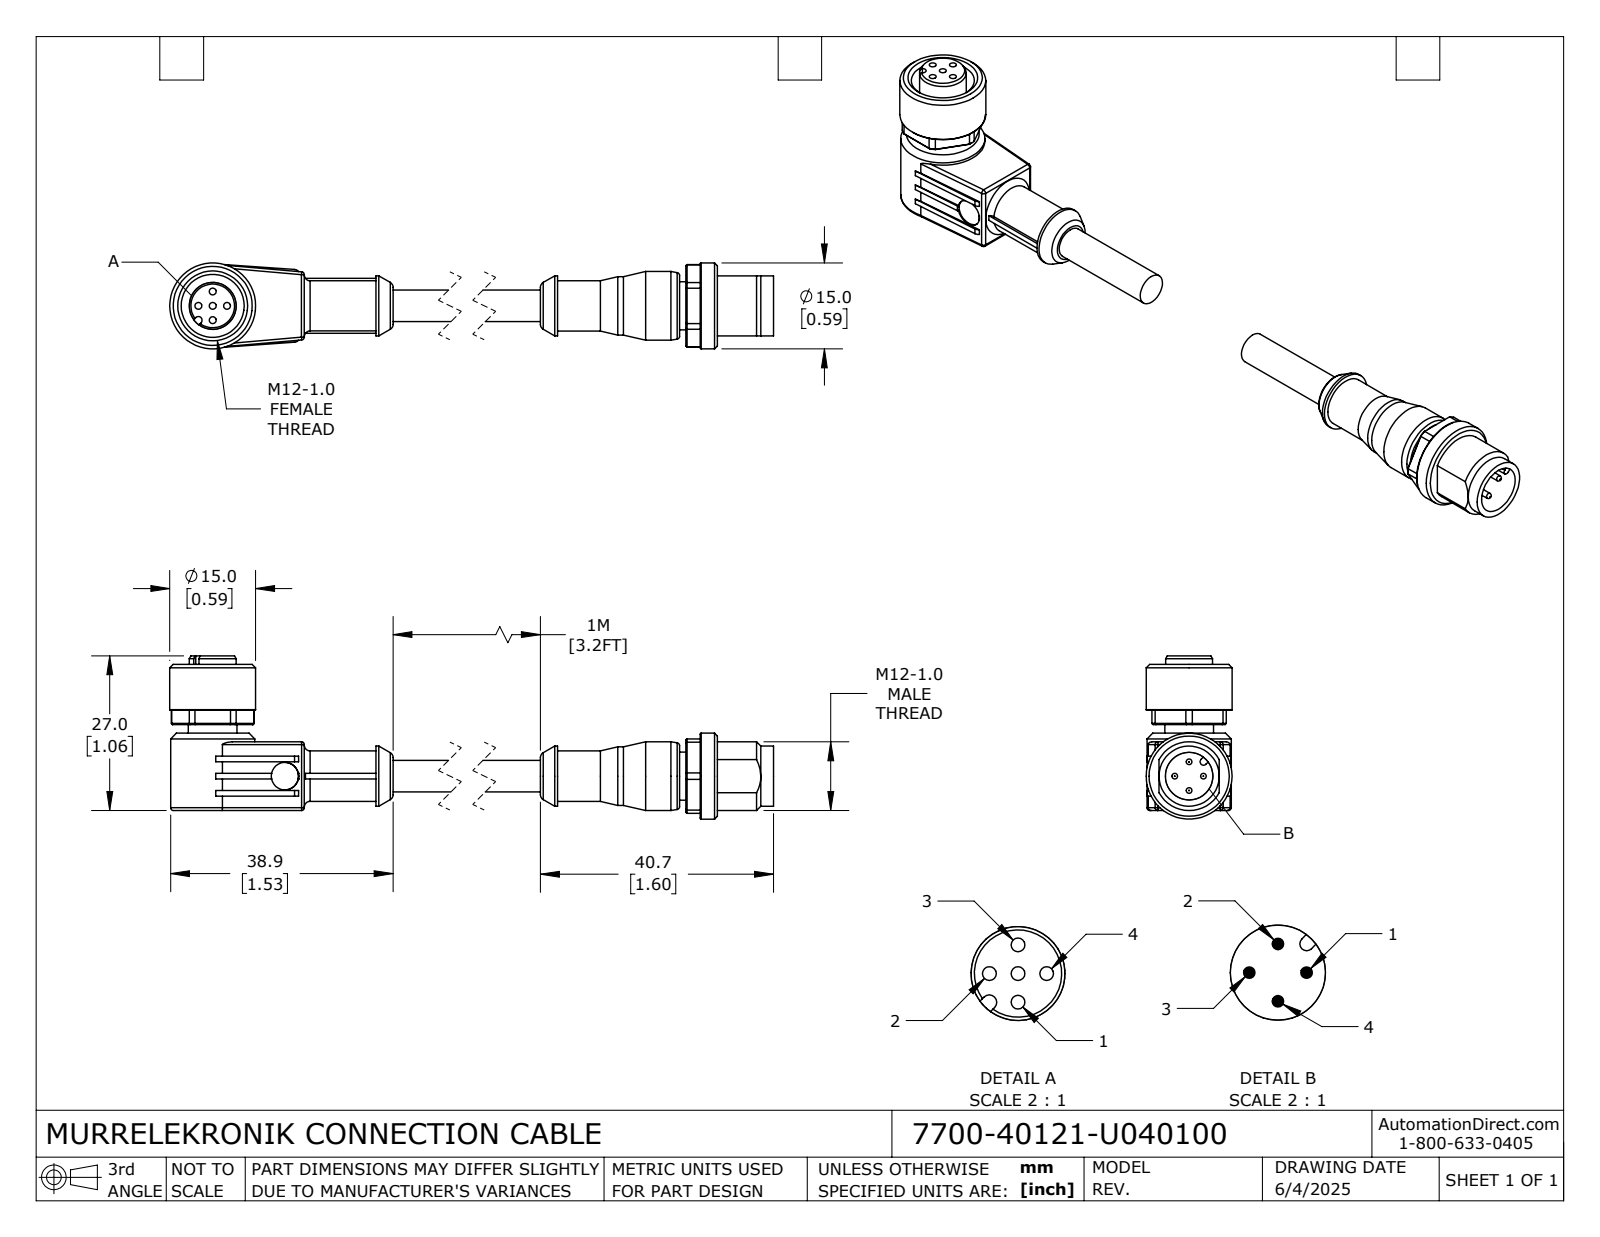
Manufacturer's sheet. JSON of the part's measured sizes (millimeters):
{"part_name": "7700-40121-U040100; 7700-40121-U040100_MALE; 7700-40121-U040100_FEMALE", "step_written_by": "SolidWorks 2024 (CONFIG_CONTROL_DESIGN)", "units": "millimeters", "bodies": {"solids": 2, "faces": 248, "planar": 91, "cylindrical": 95, "other": 62}, "overall_size": [144.7, 28.5, 15], "volume_mm3": 10768, "surface_area_mm2": 6089, "round_holes": [[1.2, 5], [4.8, 1], [8.3, 1], [11, 1]], "round_bosses_or_shafts": [[1, 4], [15, 2], [14.7, 1], [12, 1], [10.5, 1], [10.2, 1], [8.8, 1], [8.5, 1]], "partial_cylinders_radius": [[0.5, 8], [1, 2], [7.2, 2], [0.6, 1], [0.65, 1]], "face_to_face_distances": [3, 12, 1.5, 13.5, 5.5, 15, 13, 6, 10.5, 2.5], "hole_center_spacings": [2.5, 3.54, 5]}
